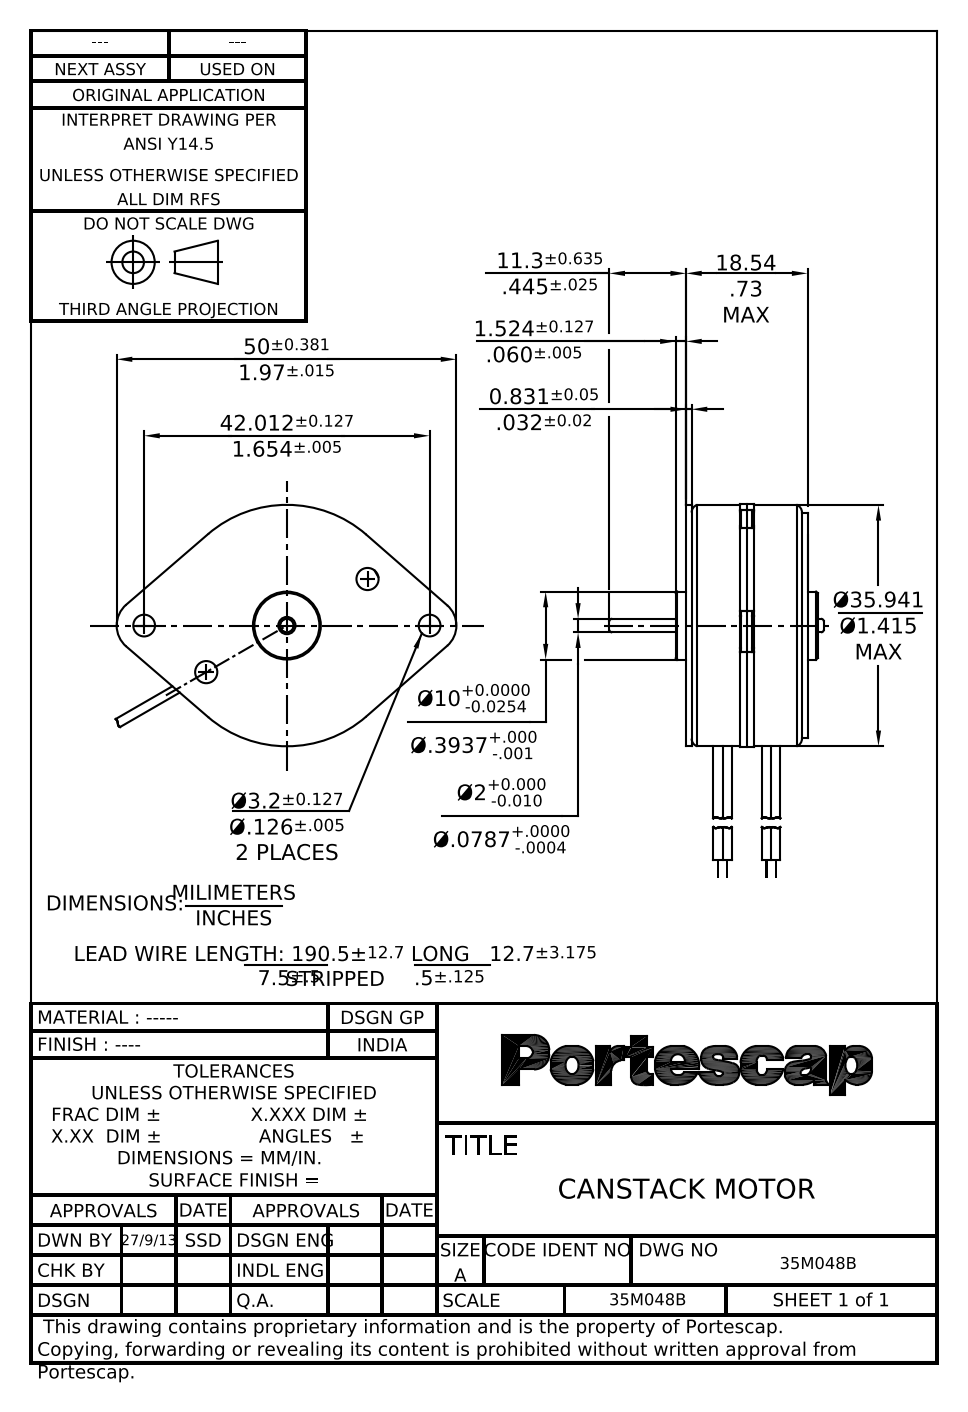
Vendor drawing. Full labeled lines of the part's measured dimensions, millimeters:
Part name (STEP PRODUCT): BREP_WITH_VOIDS_11403; MANIFOLD_SOLID_BREP_11616; MANIFOLD_SOLID_BREP_11803; MANIFOLD_SOLID_BREP_12038 (+6 more)
STEP written by: PRO/ENGINEER BY PARAMETRIC TECHNOLOGY CORPORATION, 2014310 (CONFIG_CONTROL_DESIGN)
Units: millimetres
Bodies: 8 solids, 429 faces (178 planar, 185 cylindrical, 66 other)
Overall size (bounding box): 69.6 × 44.3 × 31.6
Volume: 18 040 mm³ · Surface area: 6 371 mm²
Round holes (diameter × count): ⌀3 ×6, ⌀3.3 ×6, ⌀2.2 ×3, ⌀3 ×3, ⌀3.2 ×2, ⌀2 ×1, ⌀7.3 ×1
Round bosses / shafts (diameter × count): ⌀1.3 ×6, ⌀0.8 ×6, ⌀2.9 ×3, ⌀2.4 ×3, ⌀35.7 ×1, ⌀35.5 ×1, ⌀34.1 ×1, ⌀33.1 ×1
Partial cylindrical surfaces — rounded edges, fillets, slot ends (radius × count): R1 ×4, R1.4 ×4, R2.2 ×2, R4 ×1, R4.1 ×1, R17.8 ×1
Main face-to-face distances: 17.9, 0.8, 17.1, 16.3, 1.5, 1.6, 17.2, 18, 15.4, 3.1
Hole centre spacings: 13.7, 7.1, 19.4, 23.7, 26.5, 27.4, 11.4, 18.5
